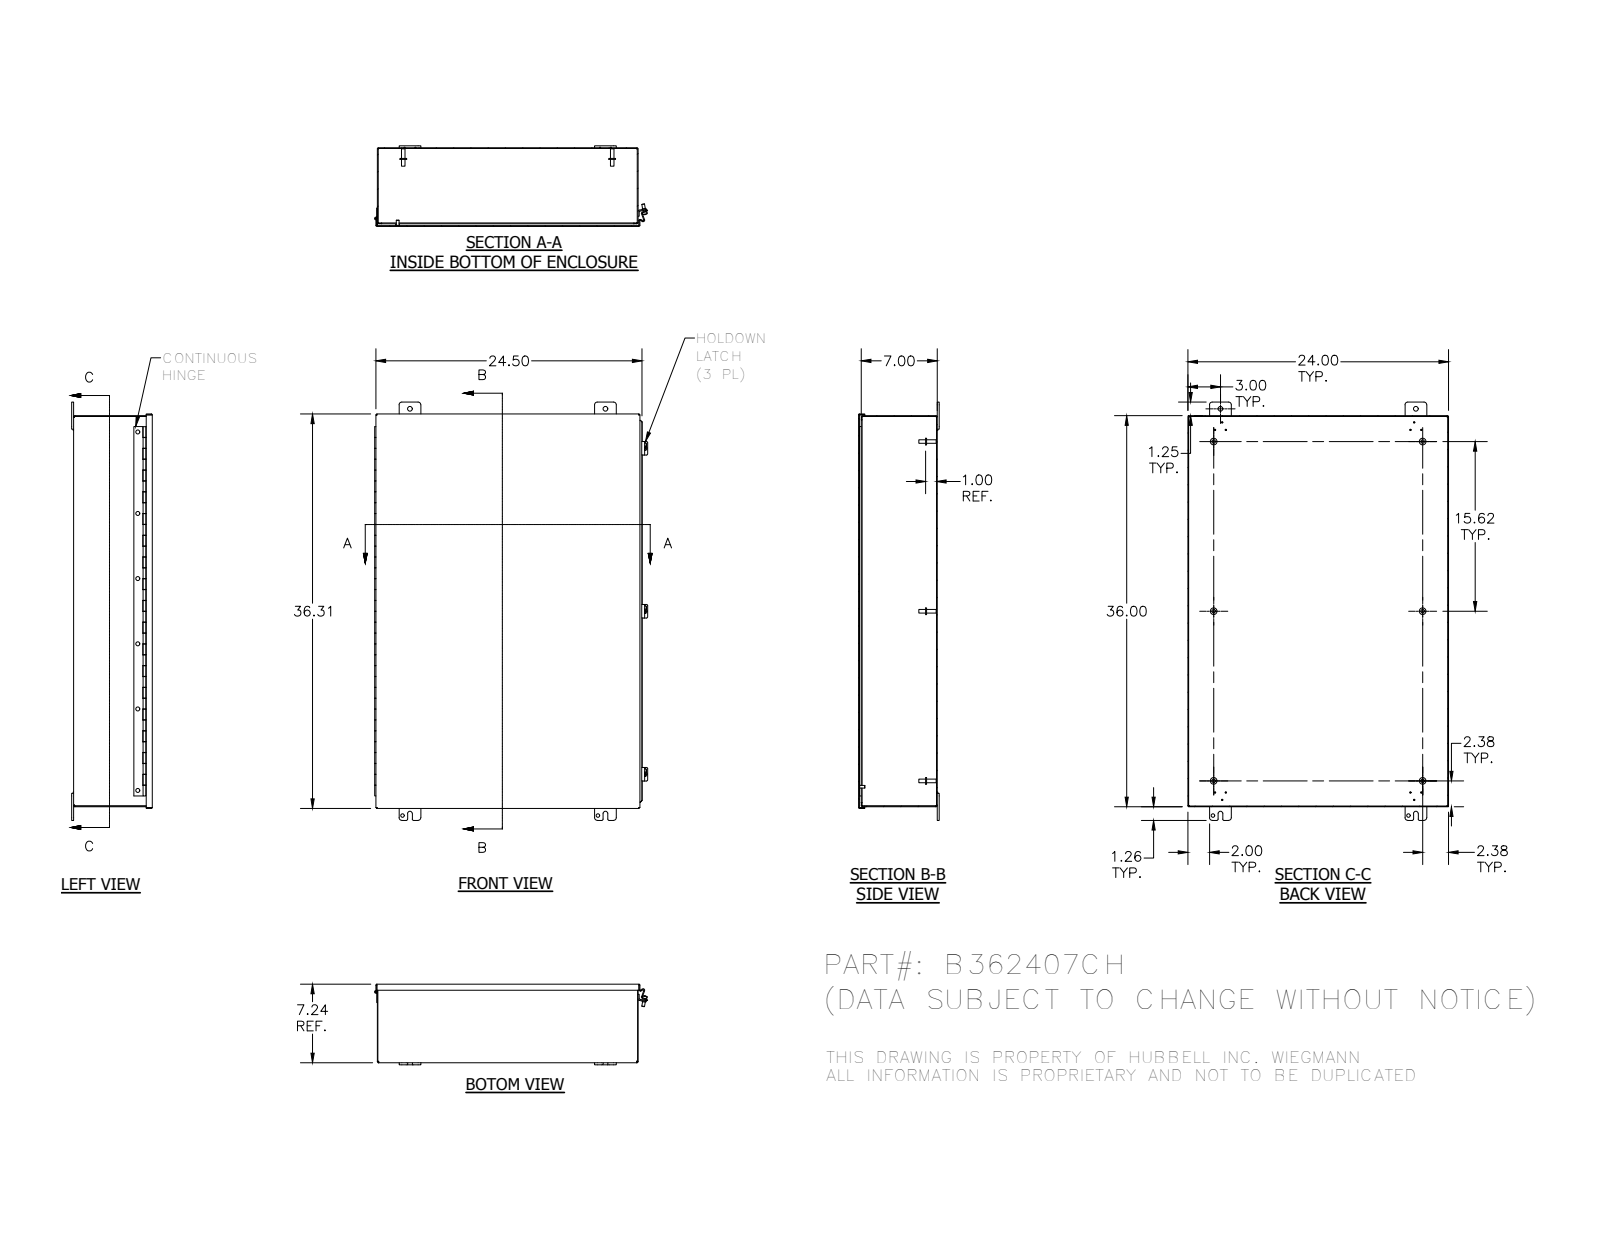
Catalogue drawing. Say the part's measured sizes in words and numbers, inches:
The part is named "B362407CH; B362407CHBKP; B3624CHLID; H6010103 (+8 more)". Its 3-D file was written by "Autodesk Inventor 2012 (AUTOMOTIVE_DESIGN)". It is 25 solids with 838 faces: 519 planar, 241 cylindrical and 78 other. Overall it measures 38.505 by 25.136 by 7.423 inches. Its volume is 207 cubic inches and its surface area 5 597 square inches. Round holes: 6 of diameter 0.11, 6 of diameter 0.375, 4 of diameter 0.313, 4 of diameter 0.438, 3 of diameter 0.196, 1 of diameter 0.125, 1 of diameter 0.125. Round bosses or shafts: 6 of diameter 0.625, 6 of diameter 0.33, 5 of diameter 0.25, 3 of diameter 0.41, 3 of diameter 0.344, 1 of diameter 0.337, 1 of diameter 0.12. Partial cylindrical surfaces (rounded edges, fillets, slot ends): 20 of radius 0.125, 16 of radius 0.25, 12 of radius 0.063, 8 of radius 0.031, 8 of radius 0.07, 8 of radius 0.105, 6 of radius 0.133, 5 of radius 0.016. The main face-to-face distances are 0.074, 7.169, 7.243, 7.095, 23.926, 35.926, 24, 23.852, 36, 35.852. The hole center spacings are 18, 15, 0.75, 6, 1.134, 1.593, 1.593, 1.881.
